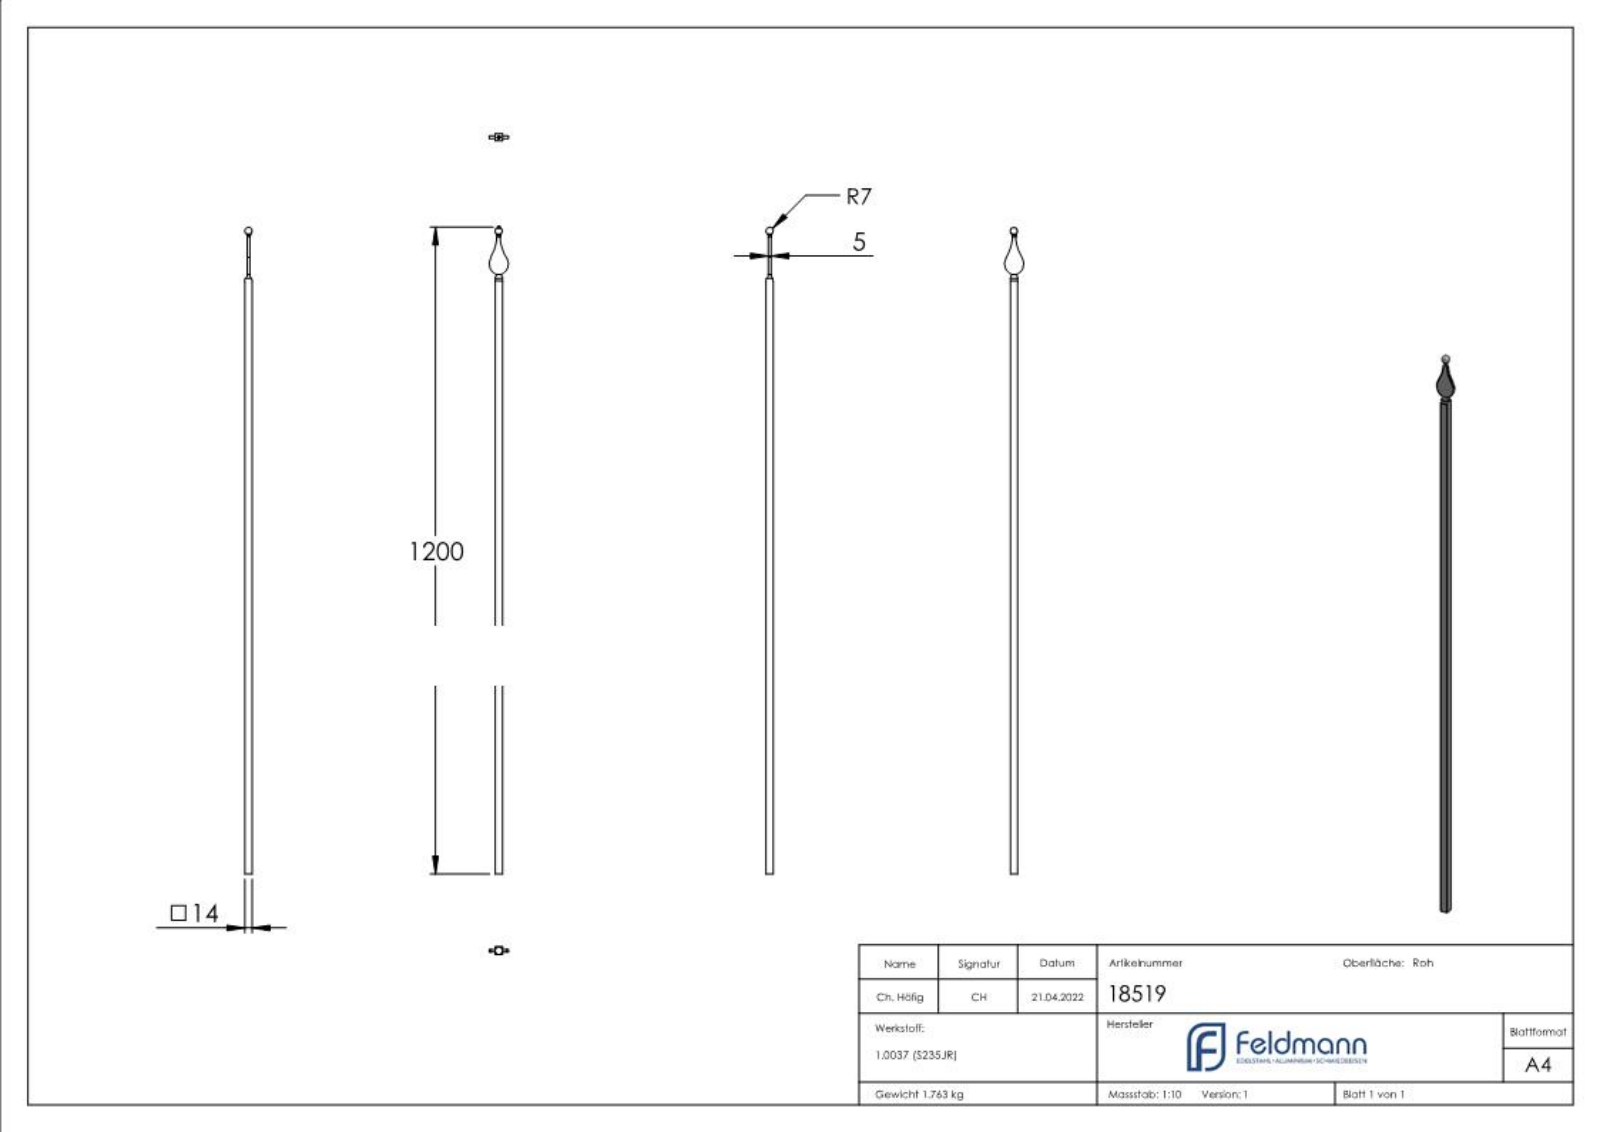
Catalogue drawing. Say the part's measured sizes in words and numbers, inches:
The part is named "18519". Its 3-D file was written by "SolidWorks 2018 (CONFIG_CONTROL_DESIGN)". It is 1 solid with 247 faces: 126 planar, 8 cylindrical and 113 other. Overall it measures 47.244 by 1.378 by 0.551 inches. Its volume is 13.8 cubic inches and its surface area 103.6 square inches. Partial cylindrical surfaces (rounded edges, fillets, slot ends): 2 of radius 0.294, 2 of radius 0.315, 2 of radius 0.394, 2 of radius 3.147. The main face-to-face distances are 0.551, 0.374, 0.177, 0.197, 0.157, 0.394, 0.236, 0.069, 0.036, 0.091.
